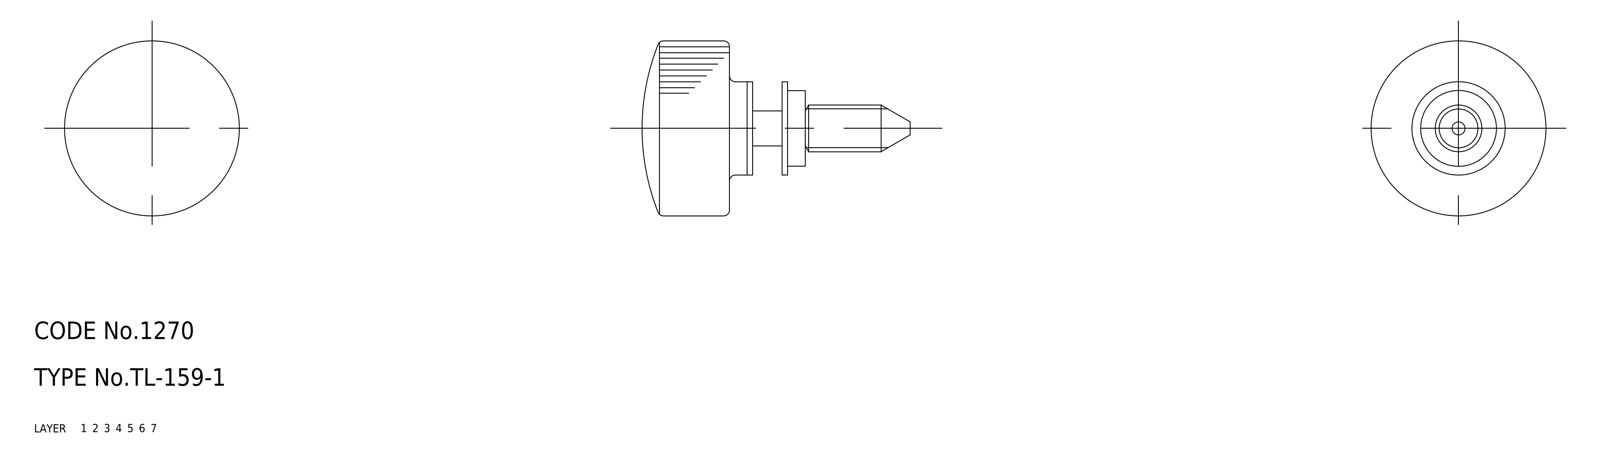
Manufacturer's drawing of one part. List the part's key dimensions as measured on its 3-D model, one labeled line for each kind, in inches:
Part name (STEP PRODUCT): washer_B; washer_A; knob; collar (+1 more)
STEP written by: CADfix (AUTOMOTIVE_DESIGN)
Units: inches
Bodies: 4 solids, 40 faces (0 planar, 0 cylindrical, 40 other)
Overall size (bounding box): 1.811 × 1.181 × 1.181
Volume: 0.724 in³ · Surface area: 6.913 in²
